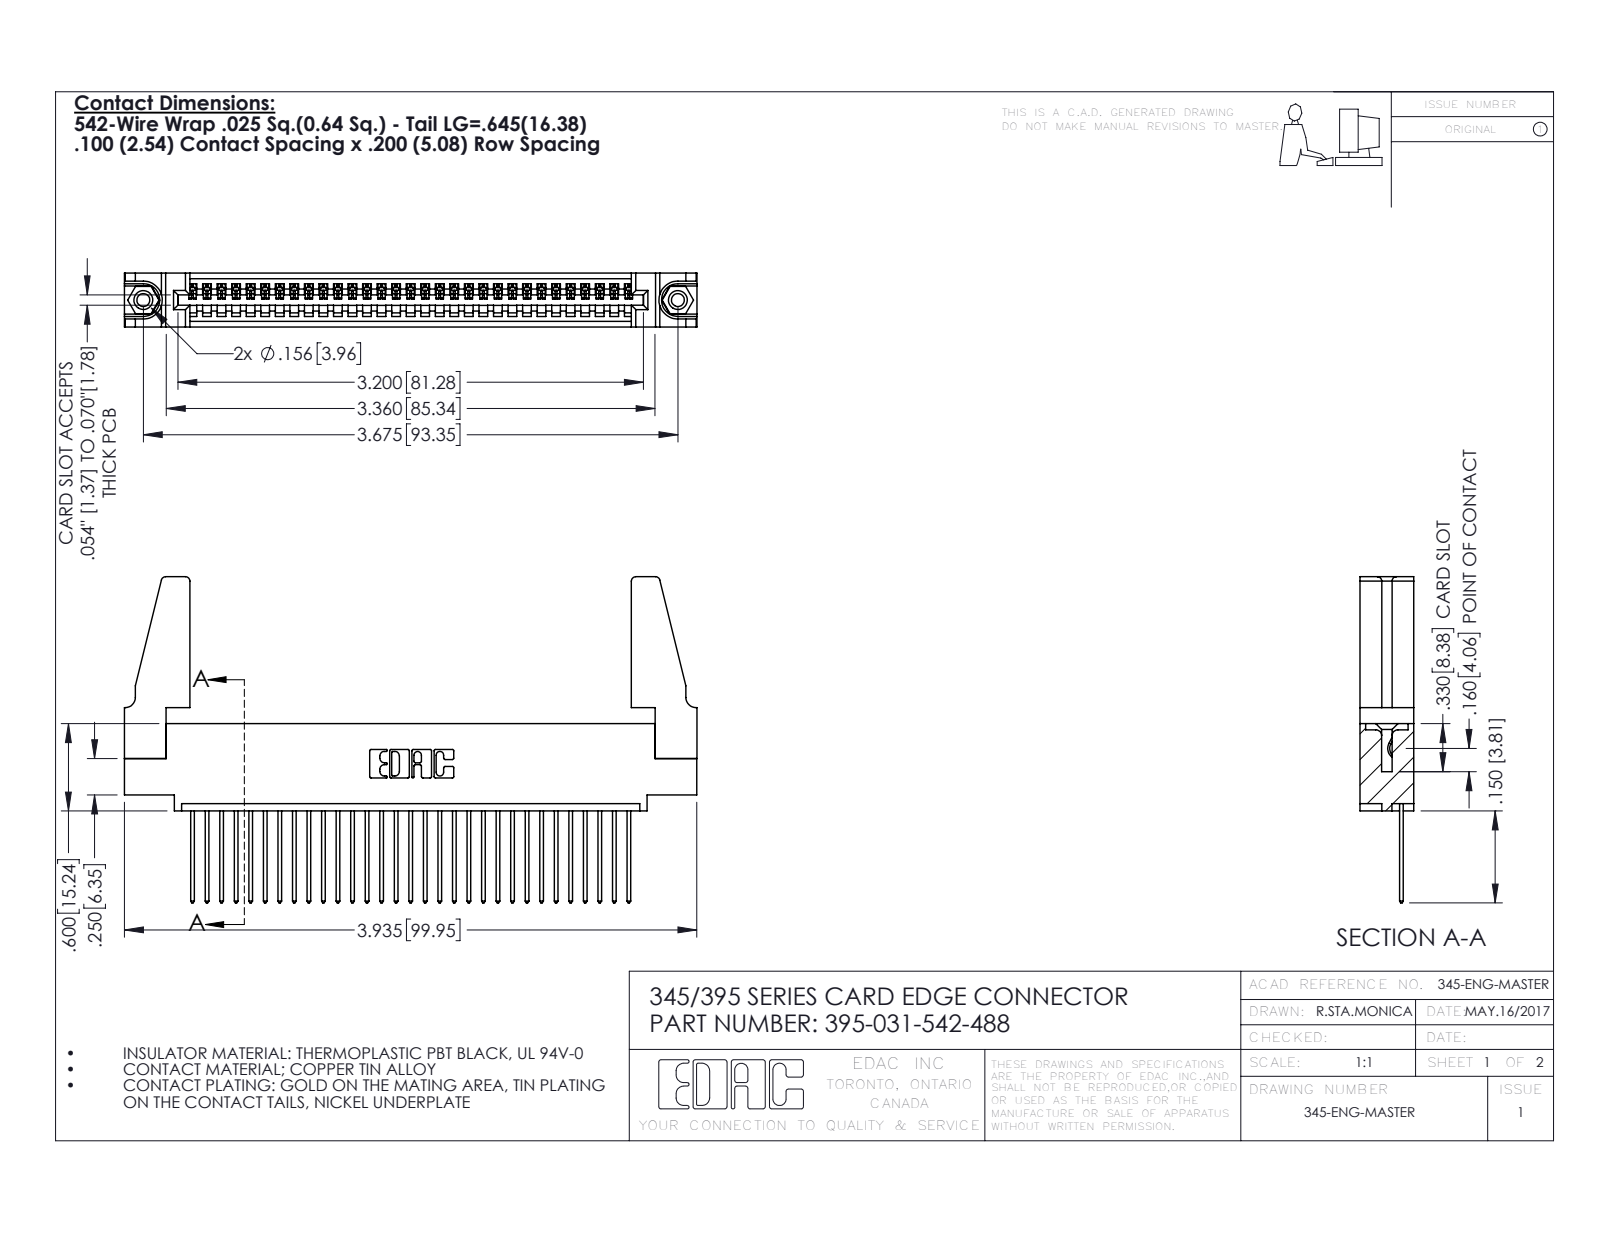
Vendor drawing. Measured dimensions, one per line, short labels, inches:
name: 345-220-078_345-220-088; 395-031-542-488; 345-292-001_345-293-142; 345 Part_0.110 Offset - 0.156 Dia-TH (+1 more)
written by: SolidWorks 2016 (CONFIG_CONTROL_DESIGN)
unit: in
bodies: 36 solids, 2052 faces (1396 planar, 640 cylindrical, 16 other)
size: 3.936 × 2.242 × 0.37
volume: 0.772 in³; area: 24.79 in²
holes: 2× ⌀0.089, 2× ⌀0.125, 2× ⌀0.156, 1× ⌀0.064
bosses: 2× ⌀0.155
rounds: 62× R0.006, 62× R0.01, 22× R0.01, 8× R0.03, 6× R0.007, 6× R0.031, 3× R0.026, 2× R0.031
face distances: 0.072, 0.298, 0.37, 0.098, 0.272, 0.025, 0.2, 0.225, 0.149, 0.072
hole spacings: 0.27, 3.44, 3.675
